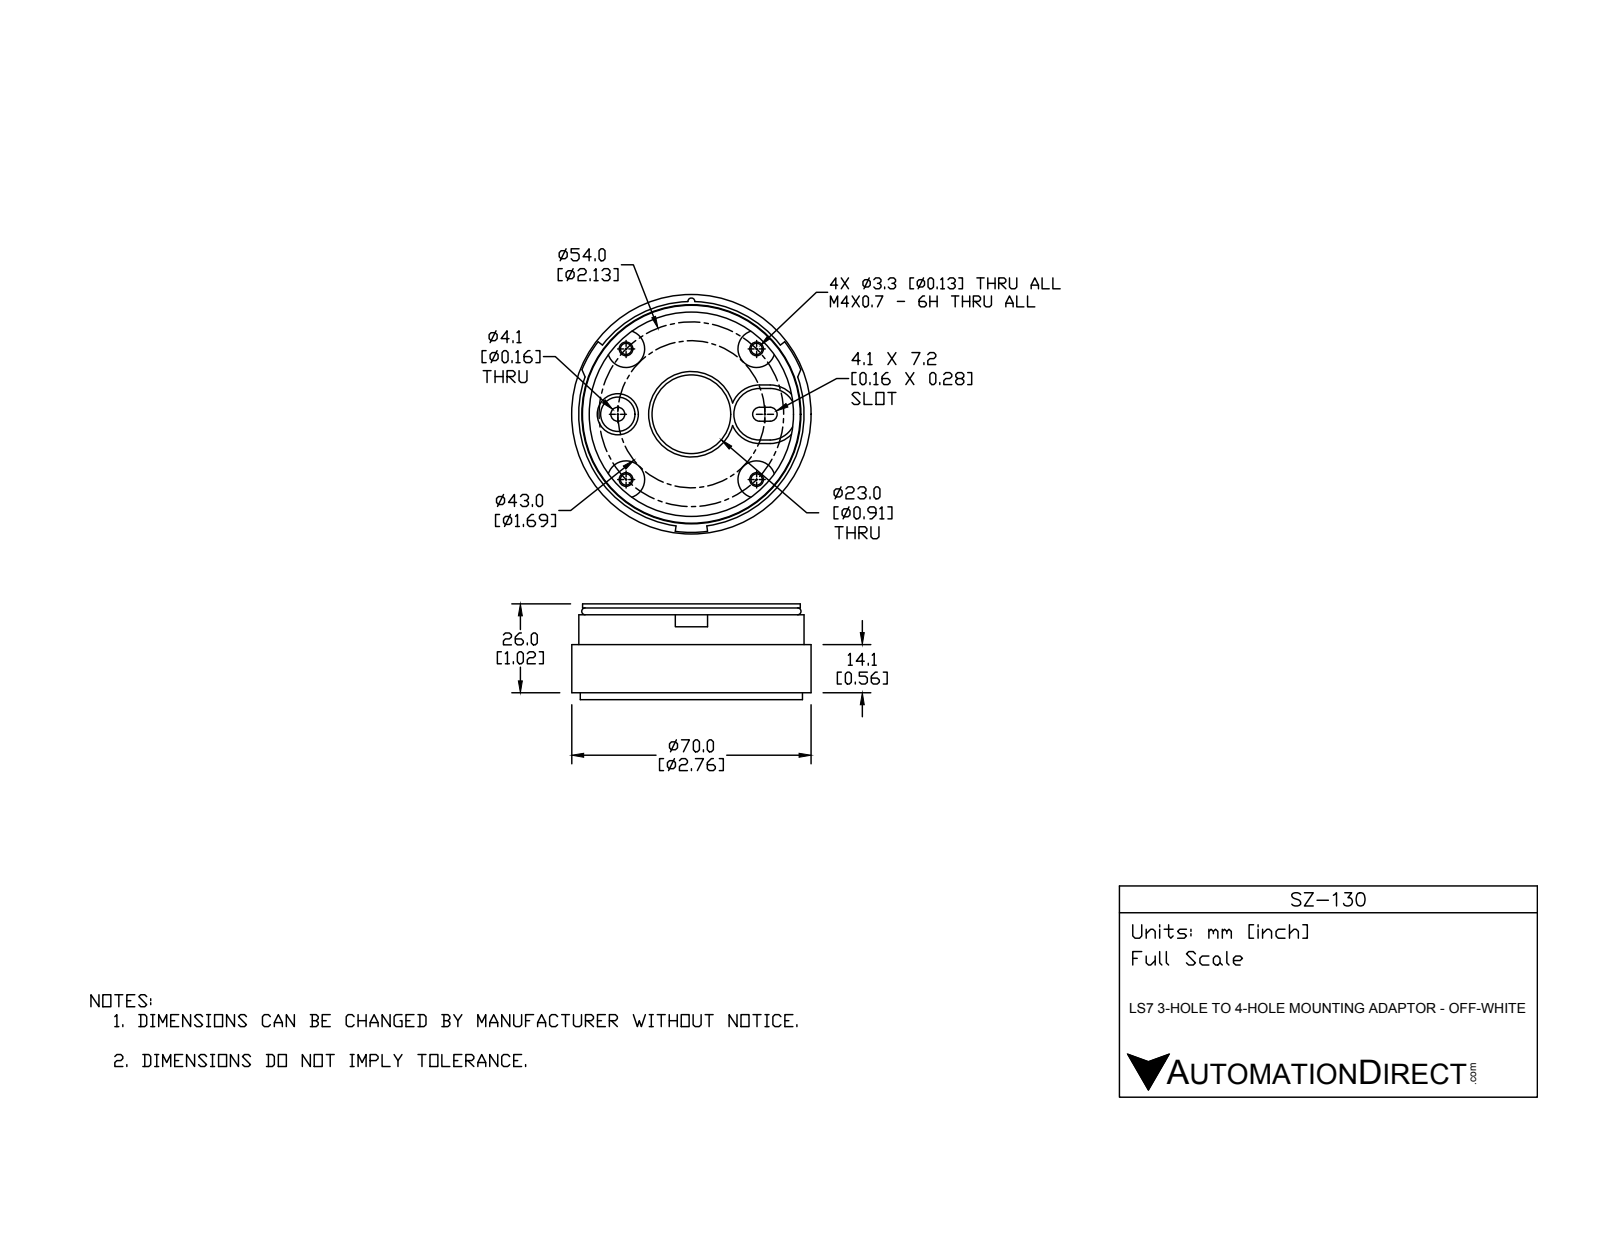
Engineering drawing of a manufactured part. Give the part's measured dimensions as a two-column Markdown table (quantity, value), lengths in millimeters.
| quantity | value |
| --- | --- |
| part name | SZ-130 |
| STEP written by | SolidWorks 2016 (AUTOMOTIVE_DESIGN) |
| units | millimeters |
| bodies | 3 solids, 132 faces (44 planar, 84 cylindrical, 4 other) |
| overall size | 70 × 70 × 28 |
| volume | 41 581 mm³ |
| surface area | 27 695 mm² |
| round holes (diameter × count) | 3.3 × 4, 4.7 × 4, 7.7 × 4, 4.1 × 1, 10 × 1, 23 × 1, 25.8 × 1, 59.72 × 1 |
| round bosses / shafts (diameter × count) | 6.7 × 4, 70 × 1, 65.9 × 1, 65 × 1, 63.7 × 1, 60.1 × 1, 25 × 1, 12 × 1 |
| partial cylindrical surfaces (radius × count) | 4.22 × 4, 5.44 × 4, 2.05 × 2, 7.55 × 2, 8.55 × 2, 1 × 1, 34.55 × 1 |
| main face-to-face distances | 2, 7.14, 5.14, 24.8, 8.7, 8.96, 22.8, 17.66, 16.1, 14.1 |
| hole center spacings | 27, 38.18, 19.24, 44.86, 53.99, 21.5 |
